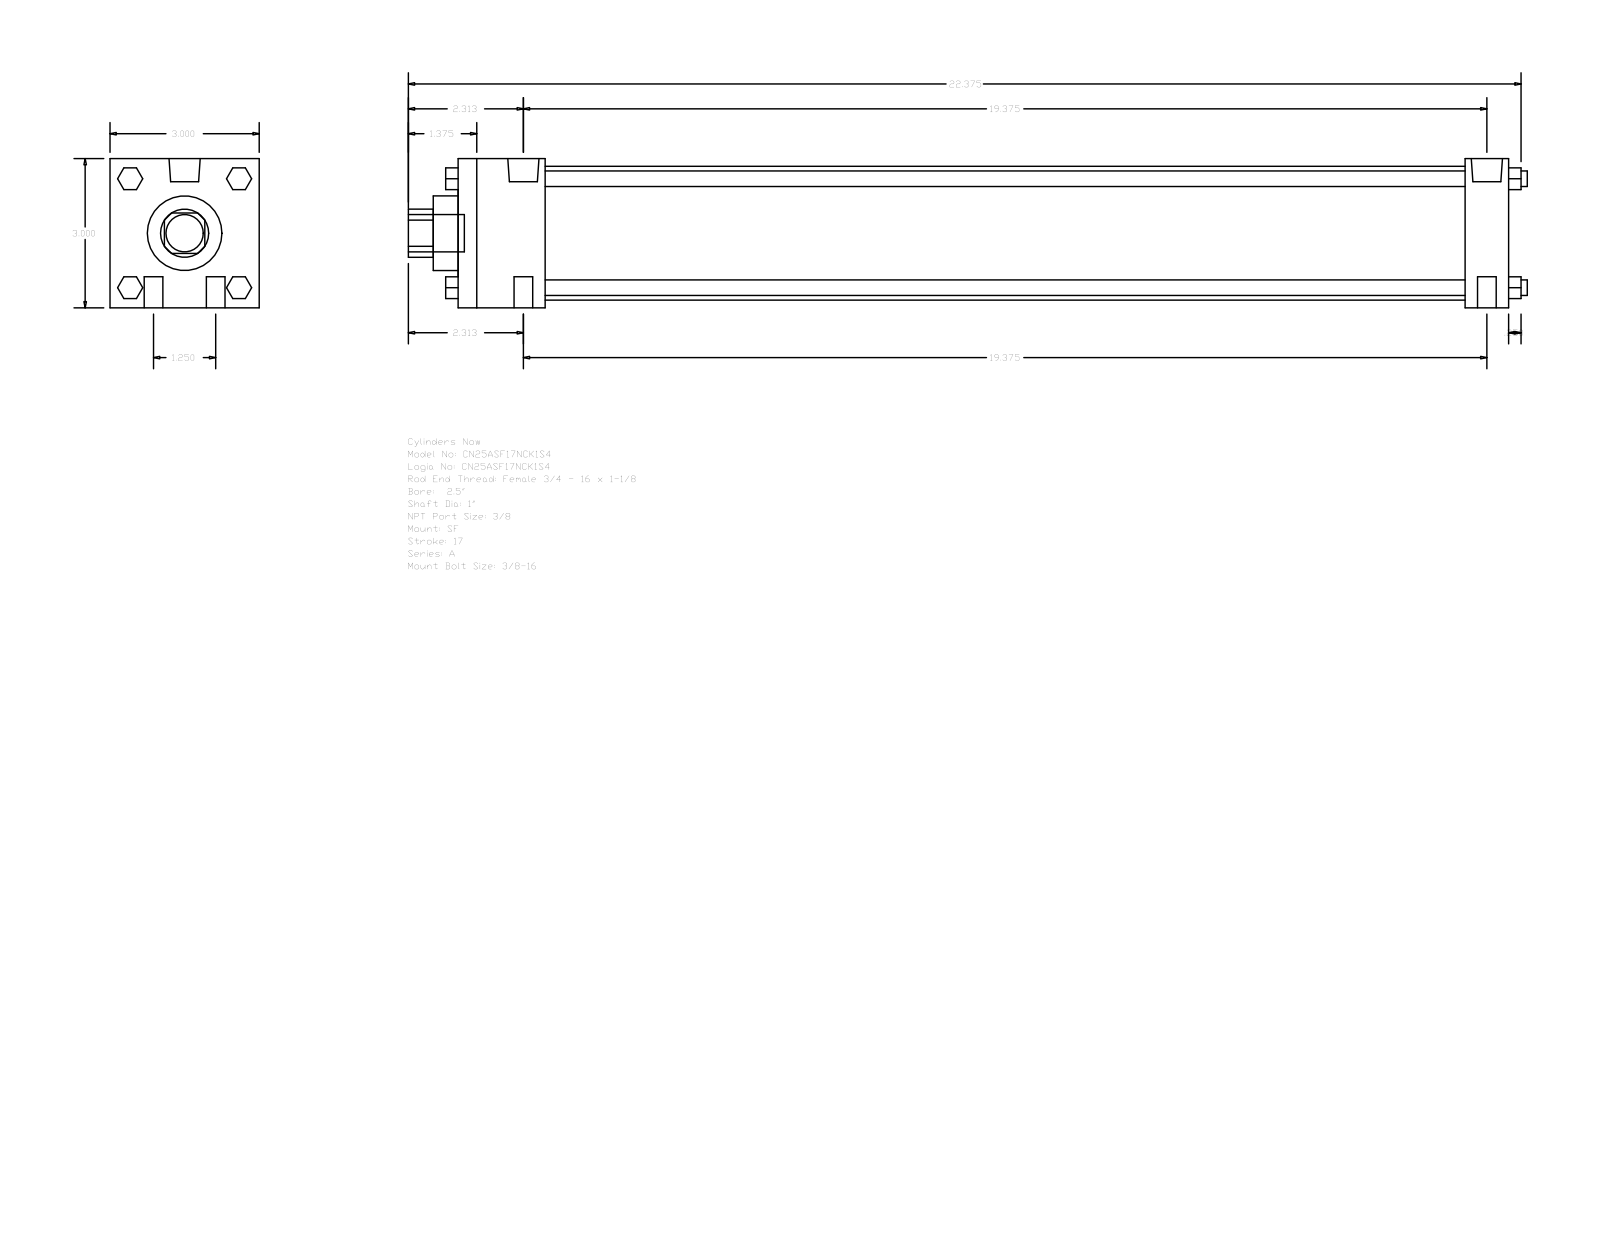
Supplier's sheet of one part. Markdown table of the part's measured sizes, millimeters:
| quantity | value |
| --- | --- |
| part name | A_SF__0250_1 |
| STEP written by | GSSL Pune (CONFIG_CONTROL_DESIGN) |
| units | millimeters |
| bodies | 0 solids, 124 faces (94 planar, 30 cylindrical, 0 other) |
| overall size | 571.5 × 76.2 × 76.2 |
| round holes (diameter × count) | 25.4 × 1, 38.1 × 1, 68.33 × 1 |
| round bosses / shafts (diameter × count) | 9.53 × 4, 7.94 × 4, 15.93 × 2, 5.56 × 2, 19.05 × 1 |
| partial cylindrical surfaces (radius × count) | 12.29 × 1 |
| main face-to-face distances | 76.2, 536.58, 514.35, 22.23, 44.45, 469.9, 492.13, 12.7, 549.28, 6.35 |
